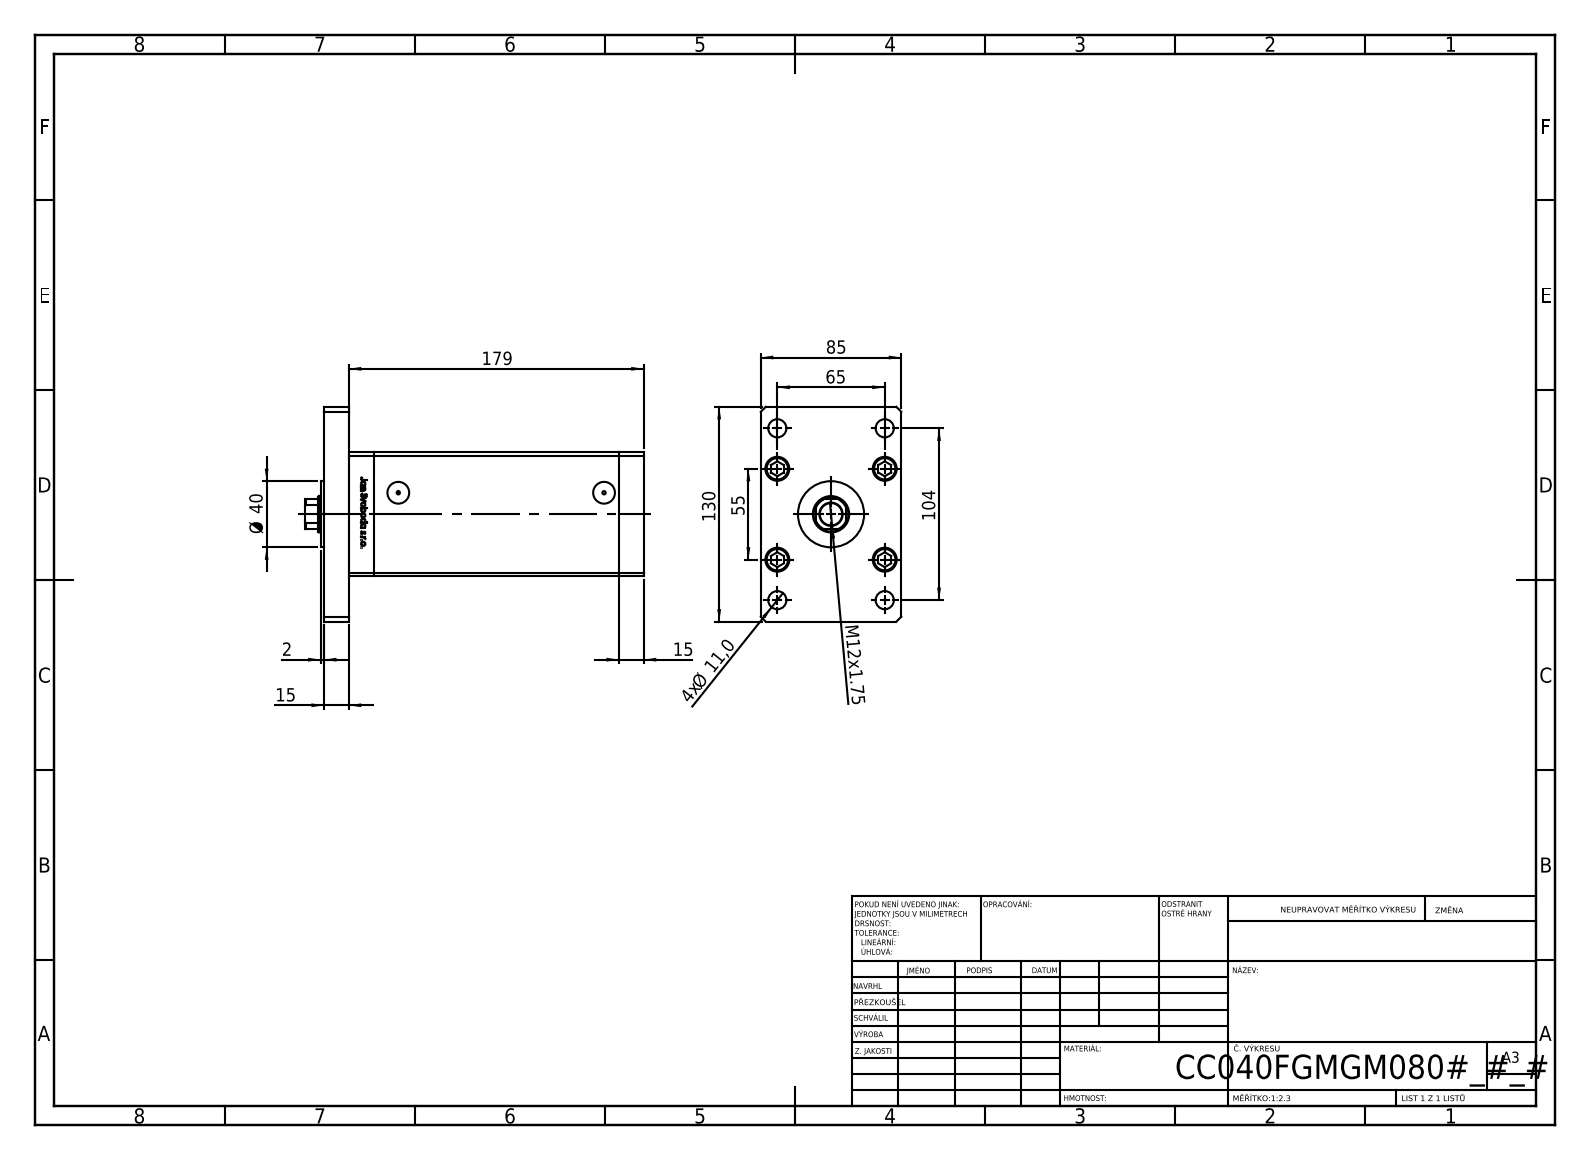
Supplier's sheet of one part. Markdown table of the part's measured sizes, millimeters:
| quantity | value |
| --- | --- |
| part name | V220C_F_MIDDLE; ALLEN BOLT; V220C BACK_F; V220C_VC_F (+2 more) |
| STEP written by | SolidWorks 2019 (CONFIG_CONTROL_DESIGN) |
| units | millimeters |
| bodies | 19 solids, 1308 faces (515 planar, 187 cylindrical, 606 other) |
| overall size | 205 × 130 × 85 |
| volume | 1 165 000 mm³ |
| surface area | 198 848 mm² |
| round holes (diameter × count) | 11 × 9, 15.5 × 5, 10 × 4, 14.5 × 4, 2 × 2, 13.16 × 2, 13.5 × 1, 22 × 1, 23.5 × 1 |
| round bosses / shafts (diameter × count) | 8 × 9, 14.5 × 5, 40 × 1 |
| partial cylindrical surfaces (radius × count) | 0.93 × 2, 10.5 × 1 |
| main face-to-face distances | 15, 85, 163.5, 178.5, 75, 148.5, 30, 193.5, 10.5, 27.5 |
| hole center spacings | 28, 24.5, 42.57, 61.32, 65, 69.46, 79.5, 102.69 |
